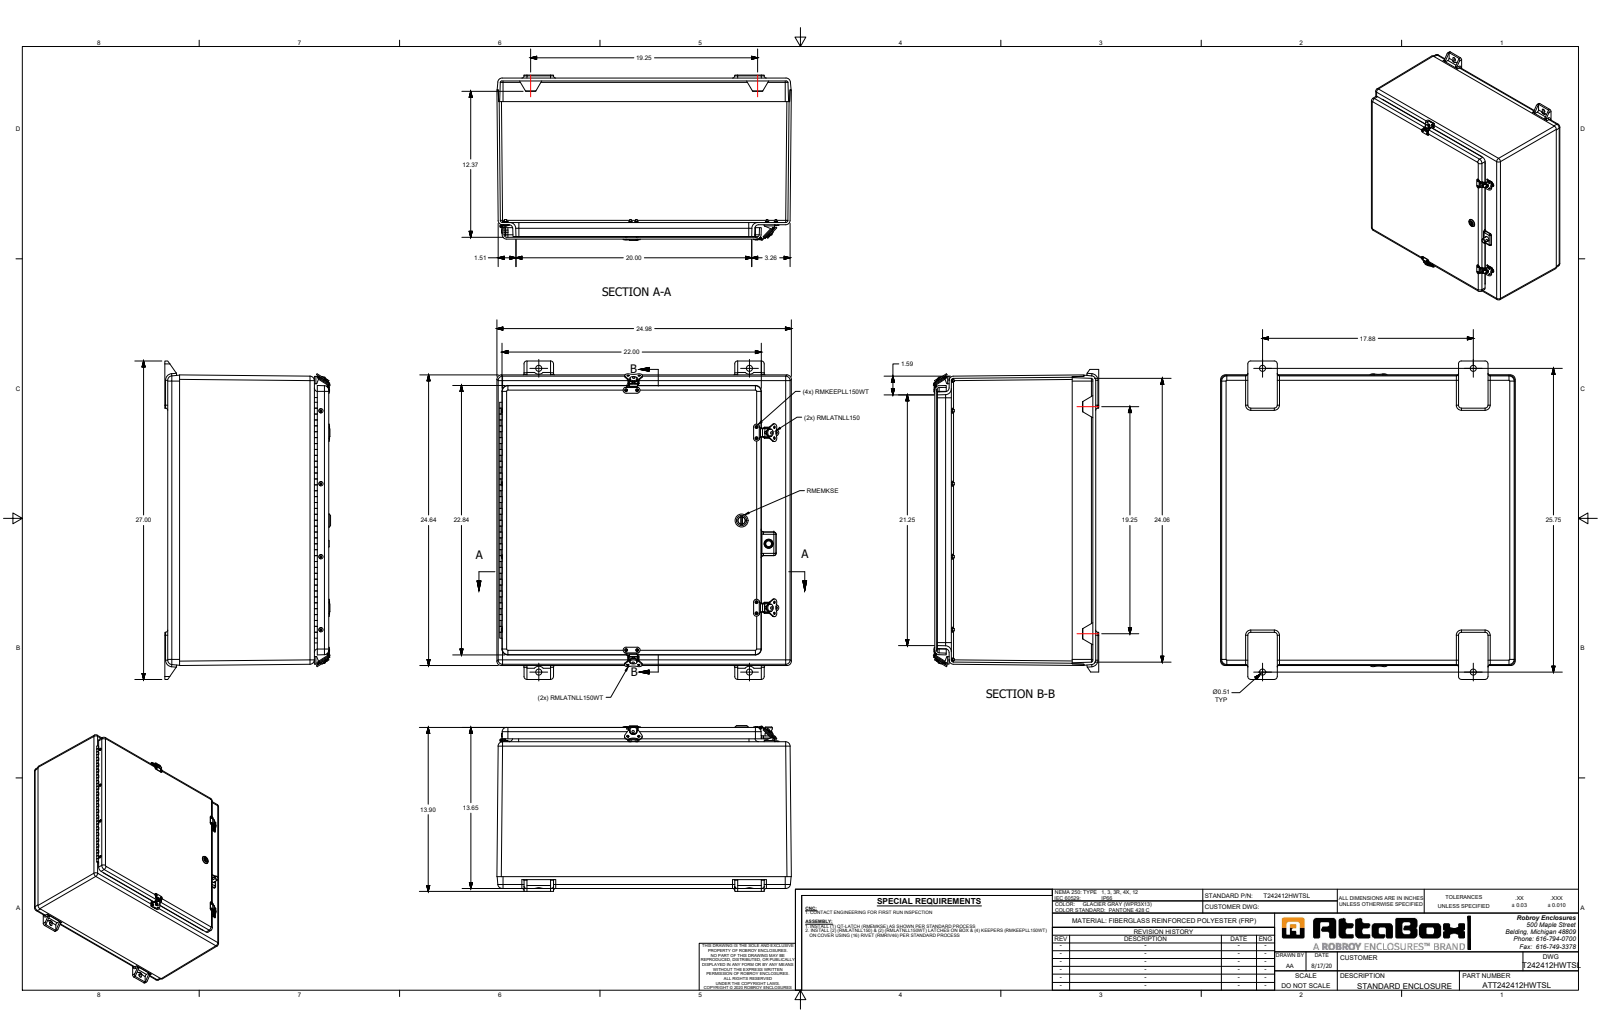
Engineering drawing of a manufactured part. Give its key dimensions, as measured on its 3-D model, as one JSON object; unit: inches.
{"part_name": "T242412HWTSL", "step_written_by": "SolidWorks 2019 (AUTOMOTIVE_DESIGN)", "units": "inches", "bodies": {"solids": 93, "faces": 1968, "planar": 906, "cylindrical": 813, "other": 249}, "overall_size": [27, 24.981, 14.061], "volume_in3": 536.5, "surface_area_in2": 5647, "round_holes": [[0.14, 16], [0.133, 12], [0.201, 12], [0.1, 10], [0.104, 8], [0.13, 8], [0.187, 8], [0.075, 6], [0.25, 5], [0.135, 4], [0.139, 4], [0.189, 4]], "round_bosses_or_shafts": [[0.125, 10], [0.357, 8], [0.283, 8], [0.187, 8], [0.66, 4], [0.582, 4], [0.525, 4], [0.438, 4]], "partial_cylinders_radius": [[0.015, 32], [0.012, 31], [0.25, 30], [0.187, 18], [0.06, 17], [0.011, 16], [0.02, 16], [0.07, 16]], "face_to_face_distances": [0.25, 0.187, 0.156, 0.188, 13.654, 13.404, 13.498, 13.248, 12.437, 1.217], "hole_center_spacings": [6.187, 0.125, 6.188, 12.375, 12.375, 18.563, 0.157, 0.85]}
